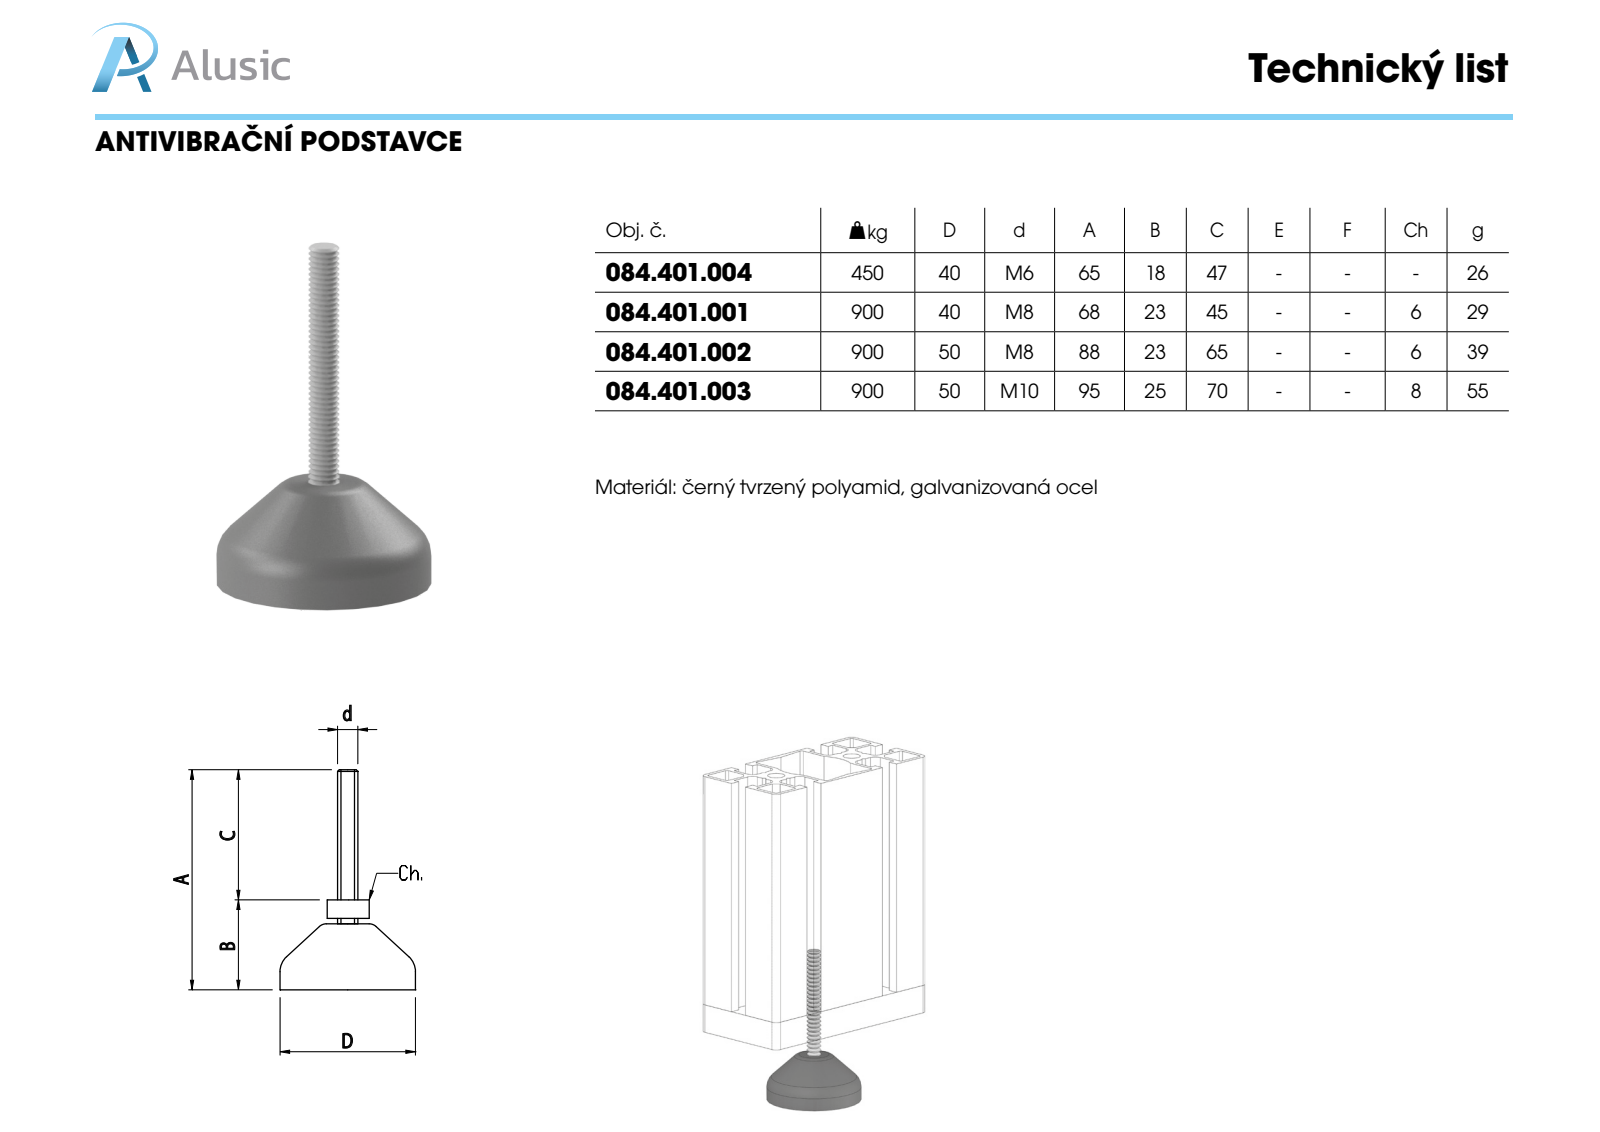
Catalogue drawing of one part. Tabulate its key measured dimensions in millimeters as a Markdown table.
| quantity | value |
| --- | --- |
| part name | 084.401.004 |
| STEP written by | SolidWorks 2011 (CONFIG_CONTROL_DESIGN) |
| units | millimeters |
| bodies | 1 solid, 15 faces (3 planar, 4 cylindrical, 8 other) |
| overall size | 65 × 40 × 40 |
| volume | 18 518 mm³ |
| surface area | 4 710 mm² |
| round bosses / shafts (diameter × count) | 40 × 1, 6 × 1 |
| main face-to-face distances | 19.5, 65, 45.5 |
